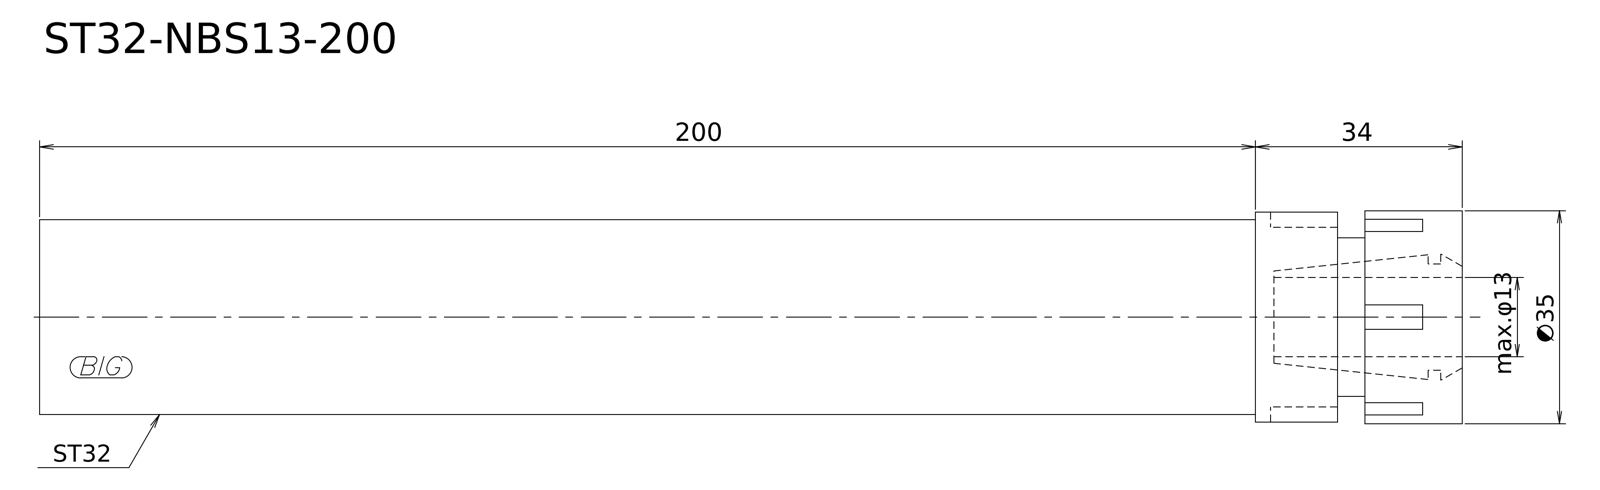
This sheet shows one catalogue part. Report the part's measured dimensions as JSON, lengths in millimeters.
{"step_written_by": "Kubotek KeyCreator V8.5.1 (14335) (CONFIG_CONTROL_DESIGN)", "units": "millimeters", "bodies": {"solids": 1, "faces": 9, "planar": 5, "cylindrical": 4, "other": 0}, "overall_size": [234, 35, 35], "volume_mm3": 191253, "surface_area_mm2": 26428, "round_bosses_or_shafts": [[35, 1], [34.5, 1], [32, 1], [26, 1]], "face_to_face_distances": [234, 16, 218, 20.5, 4.5, 213.5, 34, 18, 13.5, 200]}
